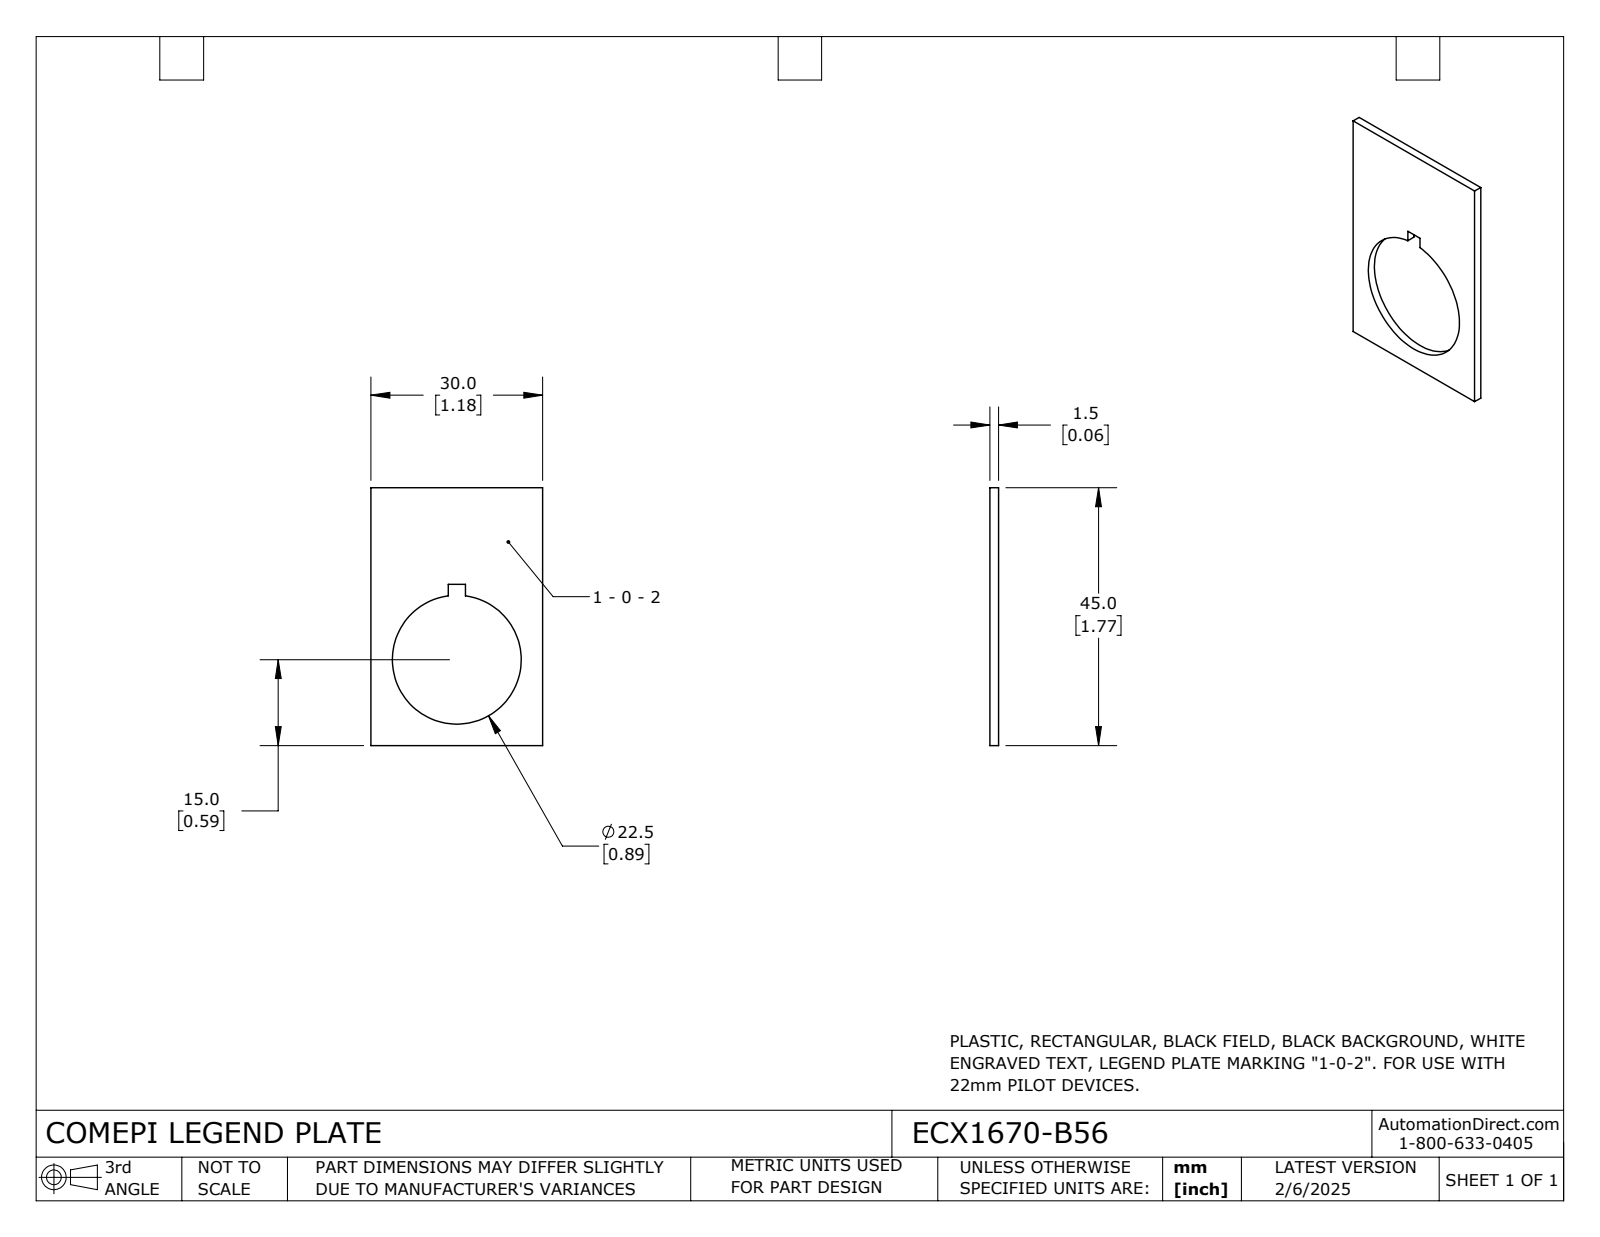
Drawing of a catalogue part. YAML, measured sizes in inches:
part_name: "ECX1670-B56"
step_written_by: "SolidWorks 2024 (CONFIG_CONTROL_DESIGN)"
units: inches
bodies: {solids: 1, faces: 12, planar: 9, cylindrical: 3, other: 0}
overall_size: [1.772, 1.181, 0.059]
volume: 0.087
surface_area: 3.457
round_holes:
  - {diameter: 0.886, count: 1}
face_to_face_distances: [0.059, 1.181, 1.772, 0.531, 0.65, 1.108, 0.663, 0.118]
